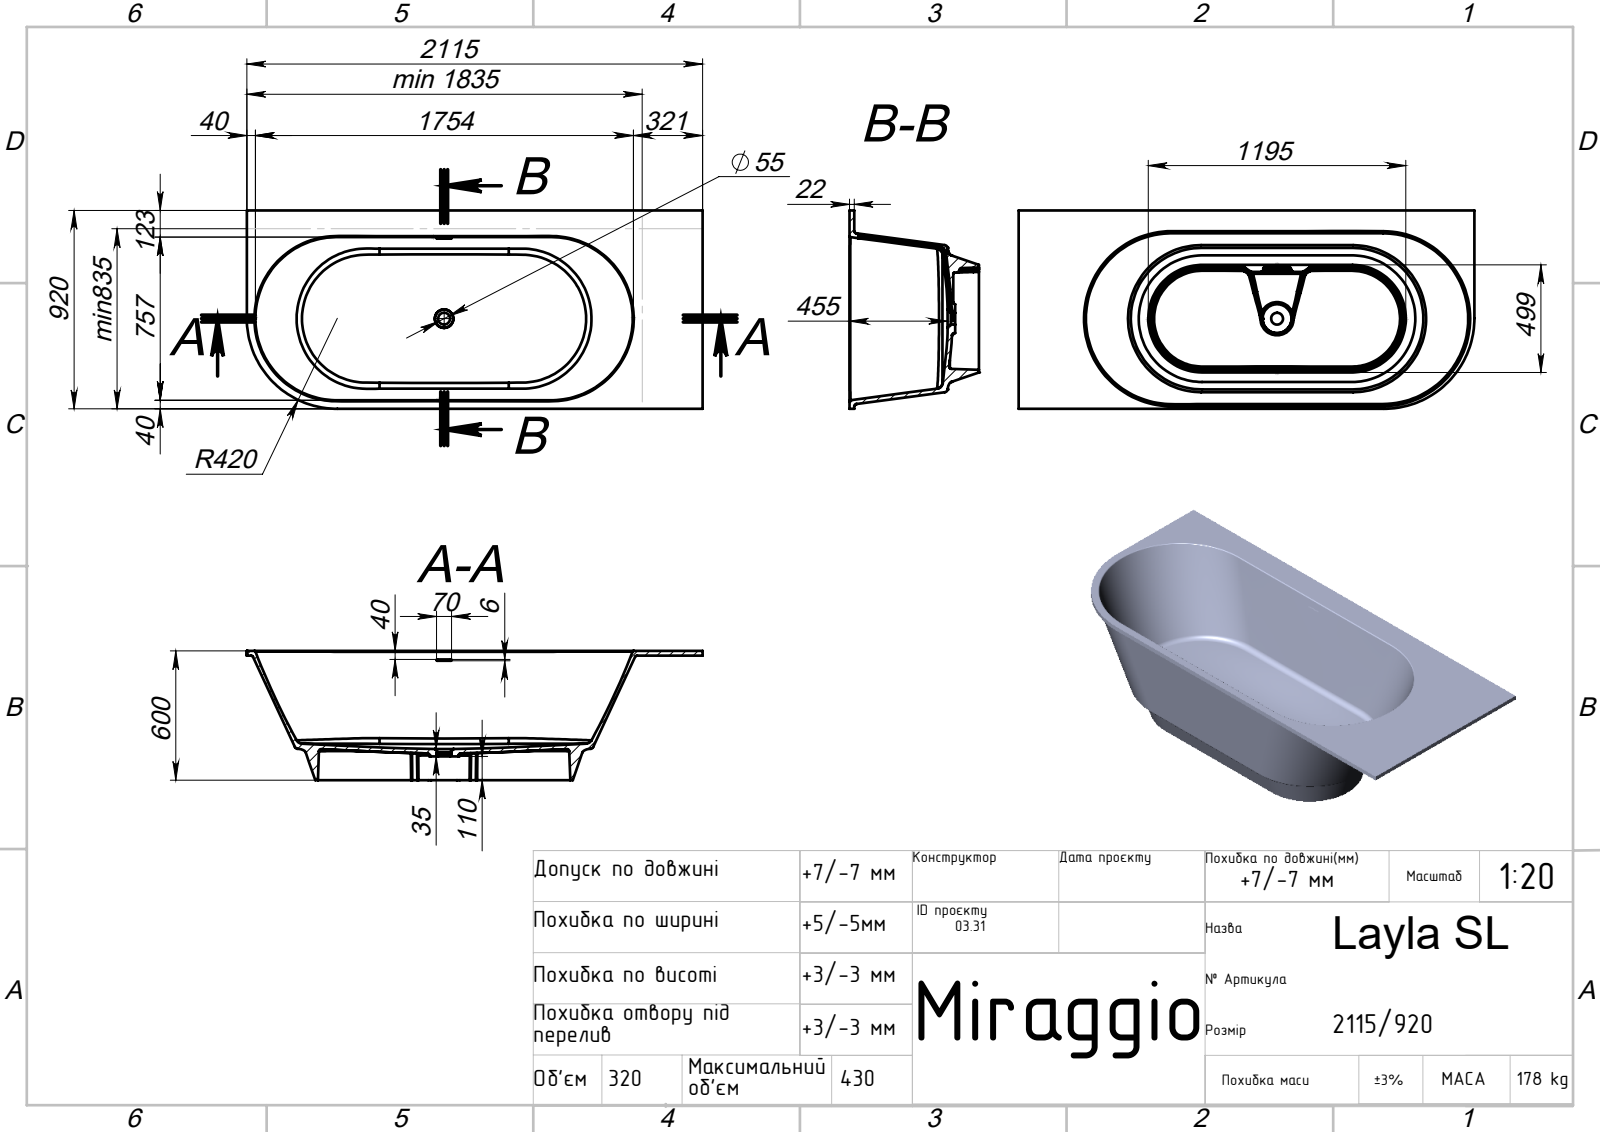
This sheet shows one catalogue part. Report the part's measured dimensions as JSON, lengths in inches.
{"part_name": "Layla SL", "step_written_by": "SolidWorks 2020 (AUTOMOTIVE_DESIGN)", "units": "inches", "bodies": {"solids": 1, "faces": 125, "planar": 28, "cylindrical": 19, "other": 78}, "overall_size": [83.268, 36.22, 23.622], "volume_in3": 4934, "surface_area_in2": 11440, "round_holes": [[2.165, 1]], "partial_cylinders_radius": [[0.394, 4], [0.197, 3], [0.118, 2], [1.457, 1], [1.811, 1], [2.461, 1], [7.818, 1], [9.341, 1]], "face_to_face_distances": [0.866, 22.756, 23.622, 36.22, 4.685, 18.071, 18.937, 4.331, 0.354, 18.425]}
